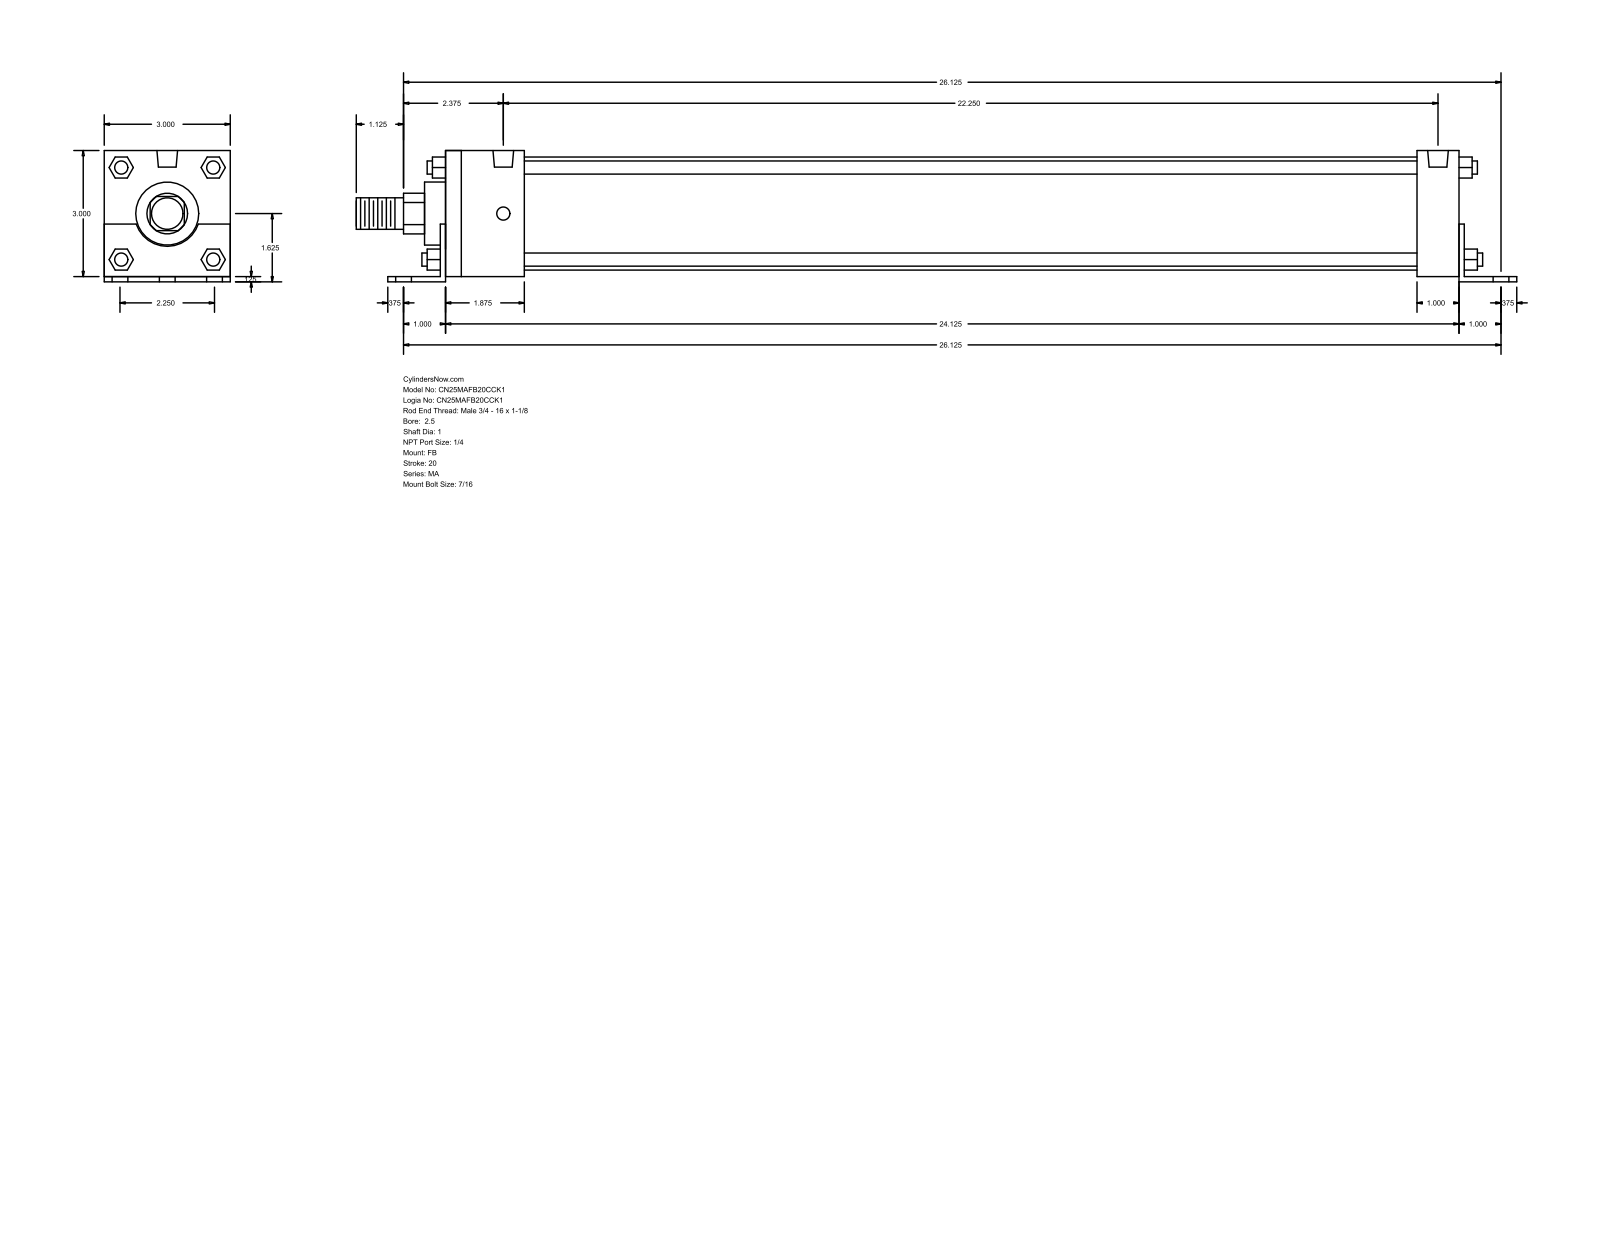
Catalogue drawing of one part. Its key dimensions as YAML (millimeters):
part_name: "MA_FB__0250_1"
step_written_by: "GSSL Pune (CONFIG_CONTROL_DESIGN)"
units: millimeters
bodies: {solids: 0, faces: 140, planar: 105, cylindrical: 35, other: 0}
overall_size: [701.67, 79.38, 76.2]
round_holes:
  - {diameter: 11.11, count: 6}
  - {diameter: 7.94, count: 4}
  - {diameter: 12.49, count: 2}
round_bosses_or_shafts:
  - {diameter: 7.94, count: 4}
  - {diameter: 68.33, count: 1}
  - {diameter: 38.1, count: 1}
  - {diameter: 25.4, count: 1}
  - {diameter: 19.05, count: 1}
partial_cylinders:
  - {radius: 12.29, count: 1}
  - {radius: 19.81, count: 1}
face_to_face_distances: [76.2, 3.17, 79.37, 612.77, 3.18, 12.7, 615.95, 25.4, 50.8, 47.63]
hole_center_spacings: [28.57, 664.19, 663.58, 47.62, 57.14, 66.75, 565.15, 603.93]
